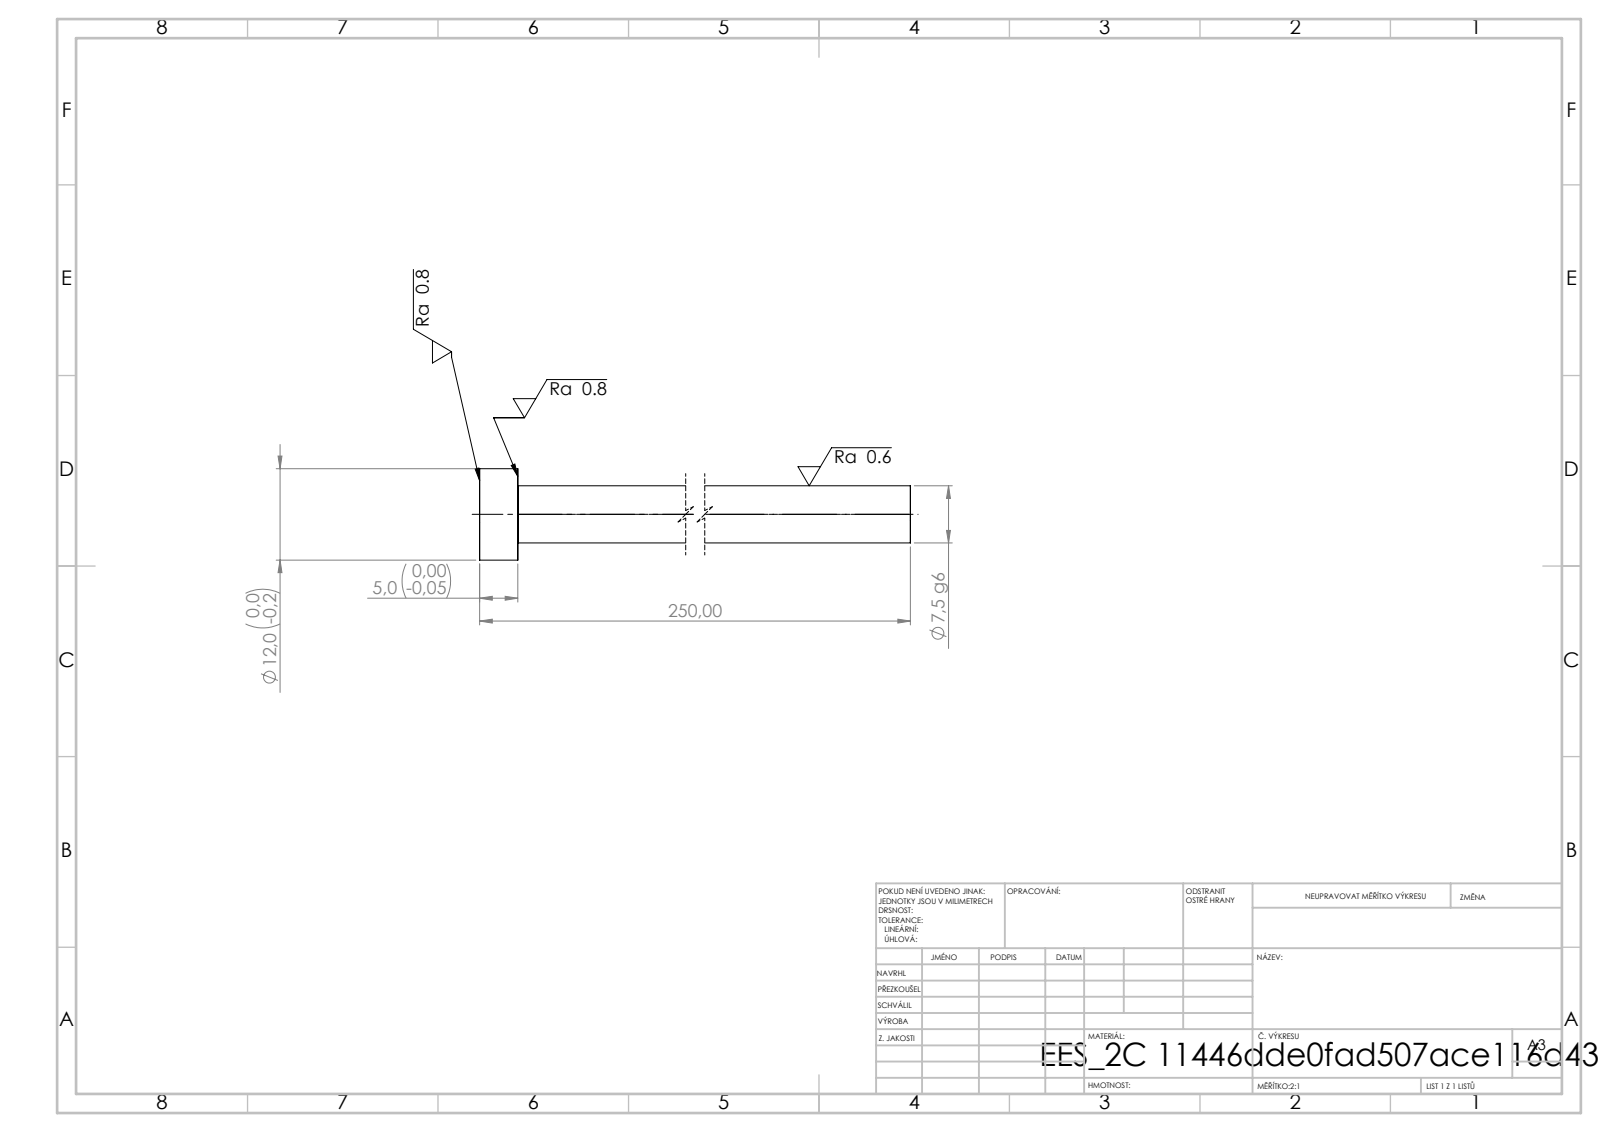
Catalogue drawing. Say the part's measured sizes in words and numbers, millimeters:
Its 3-D file was written by "SolidWorks 2019 (CONFIG_CONTROL_DESIGN)". It is 1 solid with 7 faces: 3 planar, 4 cylindrical and 0 other. Overall it measures 250 by 12 by 12 millimeters. Its volume is 11 389 cubic millimeters and its surface area 6 187 square millimeters. Round bosses or shafts: 1 of diameter 12, 1 of diameter 7.5. The main face-to-face distances are 5, 250, 245.
